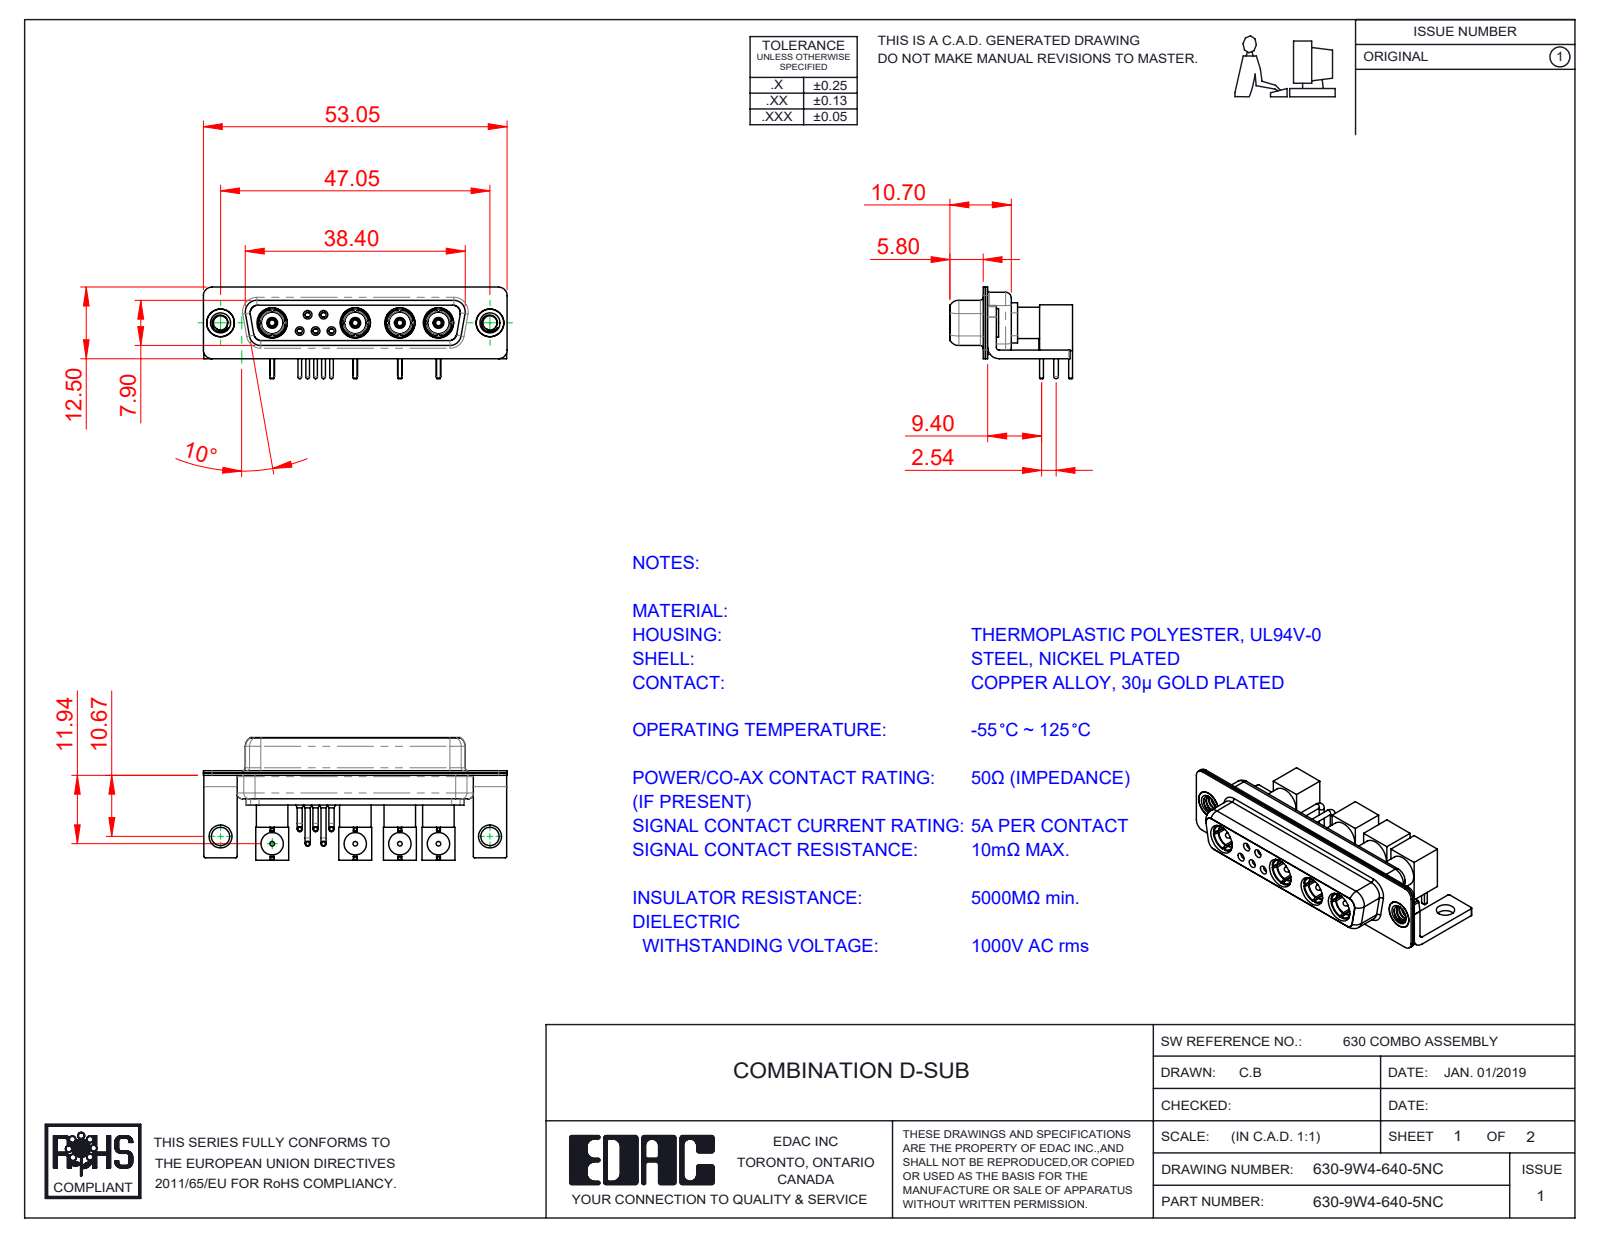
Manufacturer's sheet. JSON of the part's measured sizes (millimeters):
{"part_name": "Co-Ax Plug_RA PC Tail; Pin_RA; Insulator RA Pin; RA Back Shell (+8 more)", "step_written_by": "SolidWorks 2020 (CONFIG_CONTROL_DESIGN)", "units": "millimeters", "bodies": {"solids": 36, "faces": 1254, "planar": 430, "cylindrical": 530, "other": 294}, "overall_size": [53.05, 21.41, 16], "volume_mm3": 4948, "surface_area_mm2": 11919, "round_holes": [[1.1, 9], [1.5, 9], [4.85, 6], [0.9, 5], [2, 5], [0.8, 4], [2.83, 4], [3.1, 4], [3.3, 4], [3.9, 4], [3.92, 4], [4.1, 4]], "round_bosses_or_shafts": [[5, 6], [0.9, 5], [0.8, 5], [0.65, 5], [5.5, 4], [5.2, 4], [4.75, 4], [4.15, 4]], "partial_cylinders_radius": [[0.25, 16], [1.5, 16], [2, 13], [1.35, 8], [1.6, 8], [0.5, 5], [0.6, 4], [0.65, 4]], "face_to_face_distances": [0.4, 1.4, 1.8, 0.45, 0.8, 8.45, 8.9, 1.35, 1.85, 7.05], "hole_center_spacings": [3.16, 6.74, 7.79, 14.51, 14.52, 14.53, 22.3, 29.04]}
